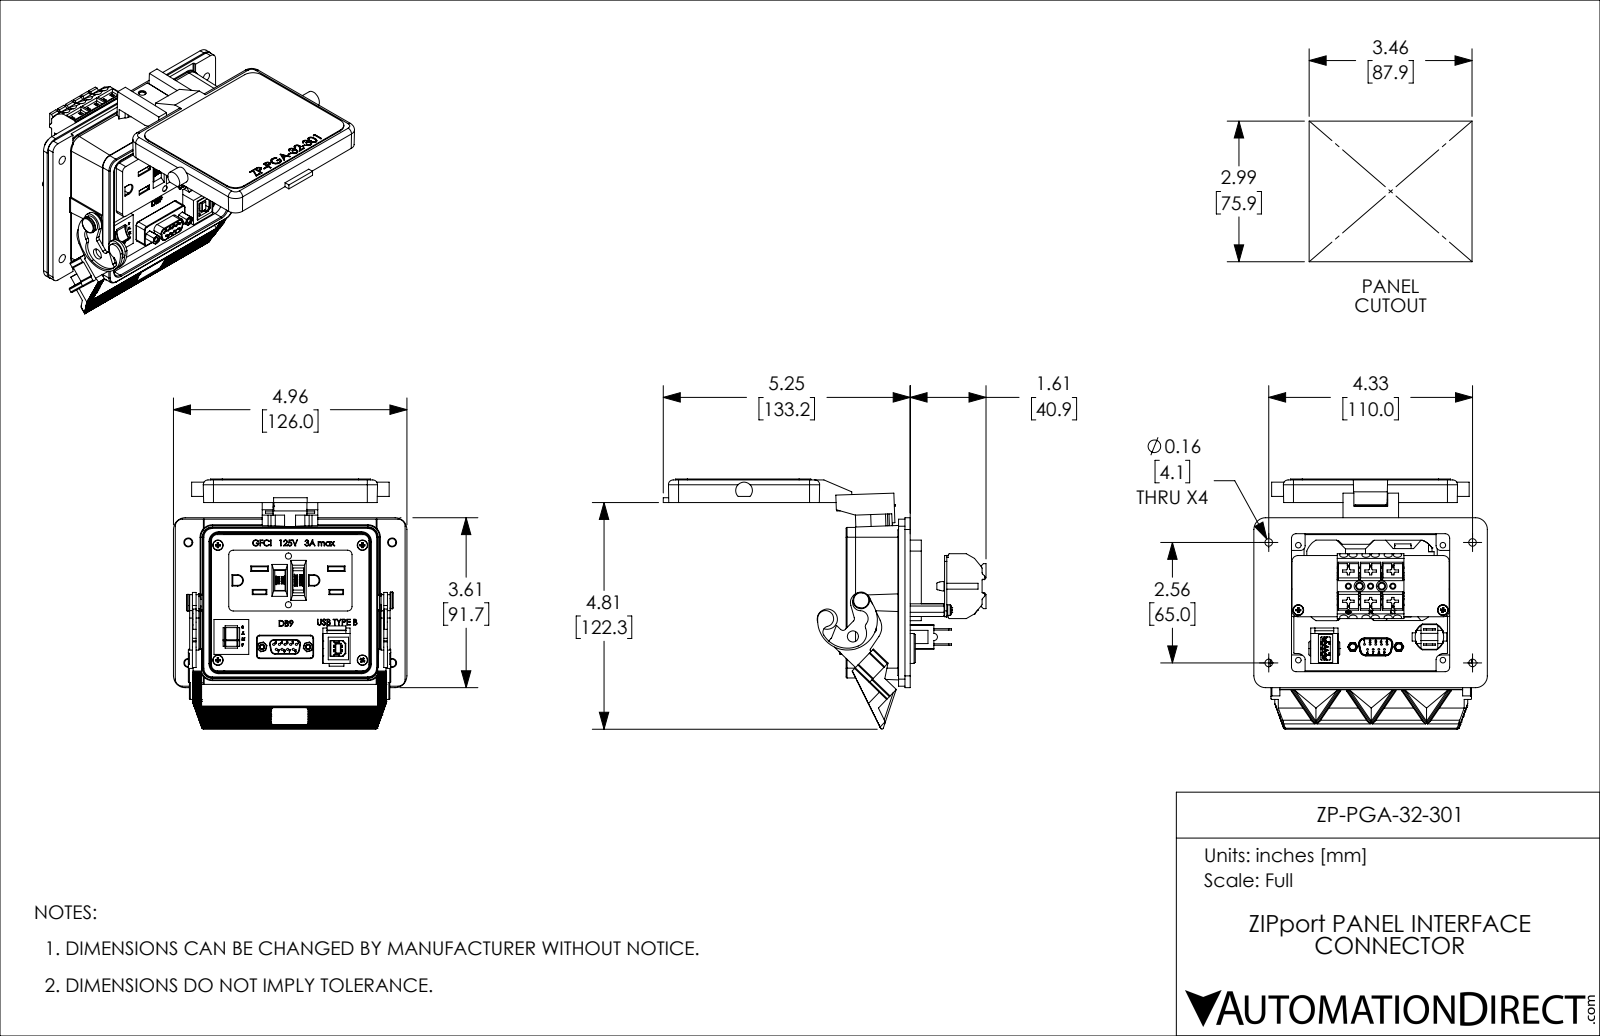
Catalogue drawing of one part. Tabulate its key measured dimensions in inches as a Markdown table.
| quantity | value |
| --- | --- |
| part name | ZP-PGA-32-301 |
| STEP written by | SolidWorks 2017 (AUTOMOTIVE_DESIGN) |
| units | inches |
| bodies | 1 solid, 4181 faces (2655 planar, 812 cylindrical, 714 other) |
| overall size | 6.857 × 5.313 × 4.96 |
| volume | 16.78 in³ |
| surface area | 199 in² |
| round holes (diameter × count) | 0.045 × 9, 0.144 × 8, 0.13 × 6, 0.138 × 6, 0.173 × 6, 0.098 × 4, 0.14 × 4, 0.16 × 4, 0.19 × 4, 0.091 × 3, 0.09 × 2, 0.097 × 2 |
| round bosses / shafts (diameter × count) | 0.038 × 9, 0.22 × 6, 0.118 × 6, 0.25 × 4, 0.205 × 3, 0.354 × 2, 0.226 × 2, 0.109 × 2 |
| partial cylindrical surfaces (radius × count) | 0.02 × 26, 0.012 × 24, 0.1 × 18, 0.02 × 17, 0.015 × 13, 0.025 × 12, 0.125 × 12, 0.25 × 12 |
| main face-to-face distances | 0.135, 0.06, 1.012, 0.765, 0.952, 0.73, 1.682, 1.742, 0.492, 0.238 |
| hole center spacings | 0.12, 0.472, 0.125, 0.236, 0.633, 1.063, 1.287, 1.378 |
